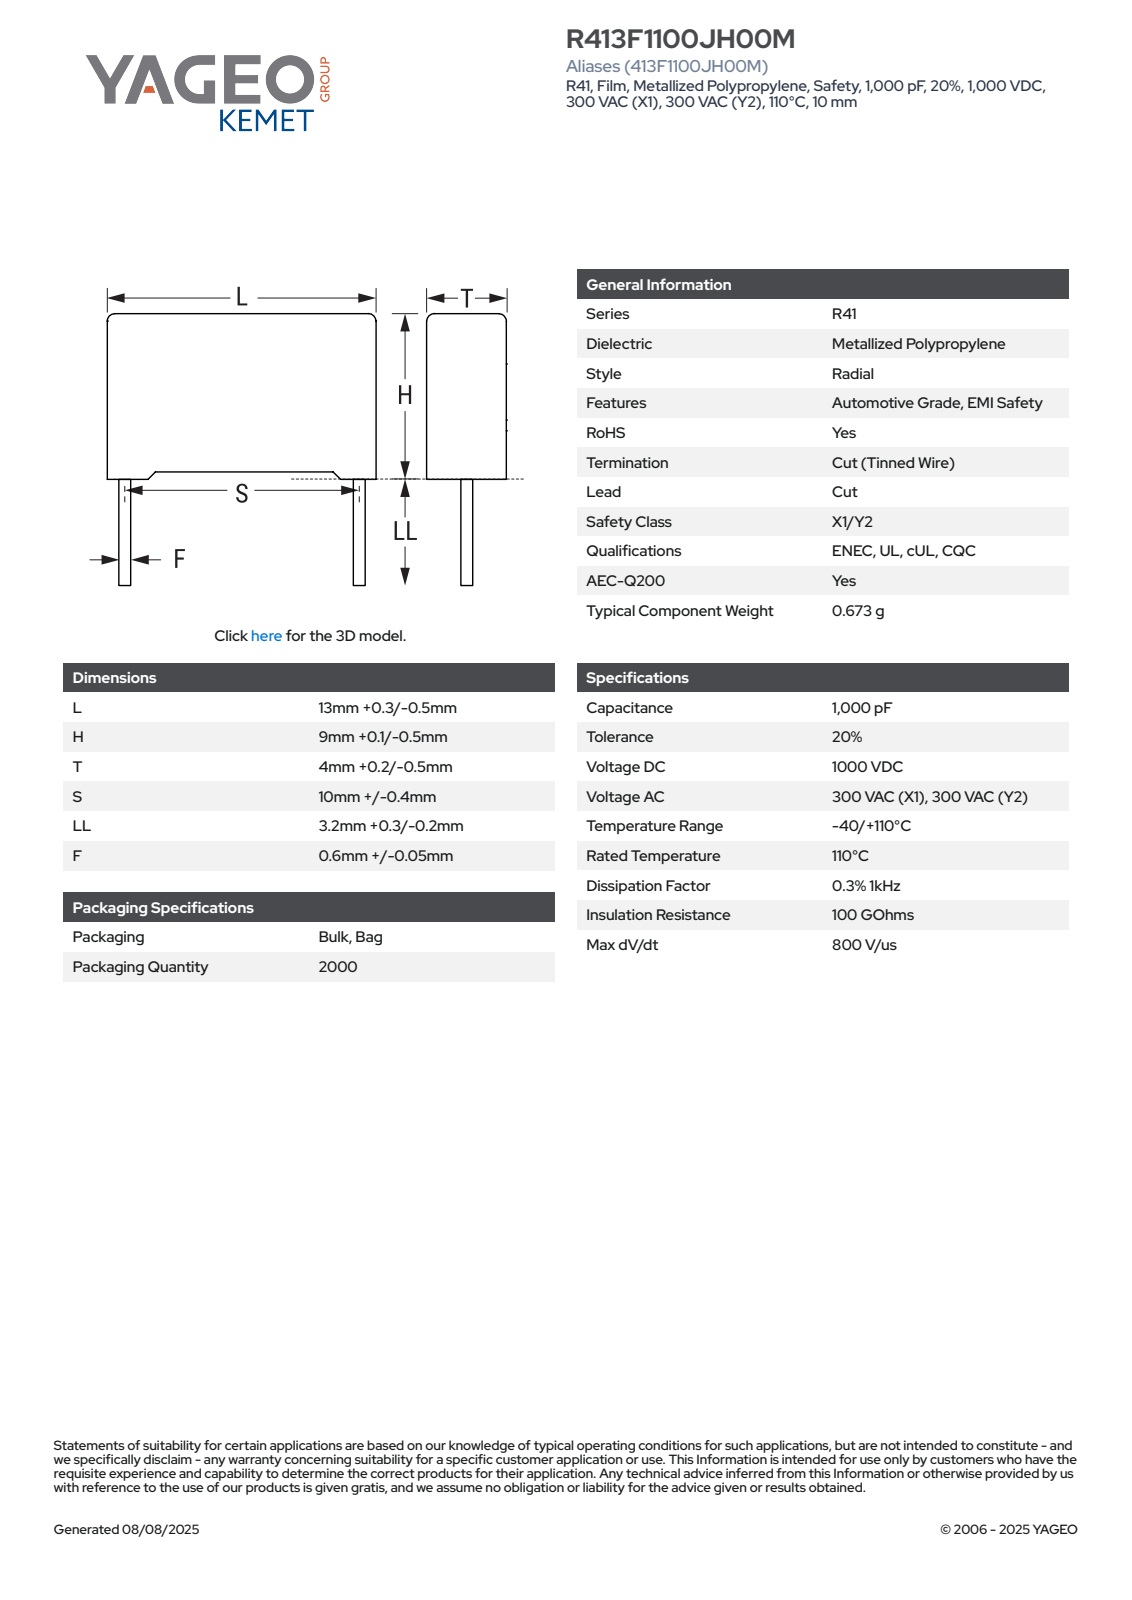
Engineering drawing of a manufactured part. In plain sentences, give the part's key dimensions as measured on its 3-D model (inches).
The part is named "CFR_RB2_13X9X4_L13.3H9.1T4.2S10LL3.5F0.65". Its 3-D file was written by "SolidWorks 2021 (AUTOMOTIVE_DESIGN)". It is 4 solids with 85 faces: 77 planar, 8 cylindrical and 0 other. Overall it measures 0.524 by 0.496 by 0.166 inches. Its volume is 0.029 cubic inches and its surface area 0.727 square inches. Round bosses or shafts: 2 of diameter 0.026. Partial cylindrical surfaces (rounded edges, fillets, slot ends): 4 of radius 0.02. The main face-to-face distances are 0.165, 0.329, 0.524, 0.017, 0.148, 0.03, 0.358, 0.131, 0.012, 0.346.
